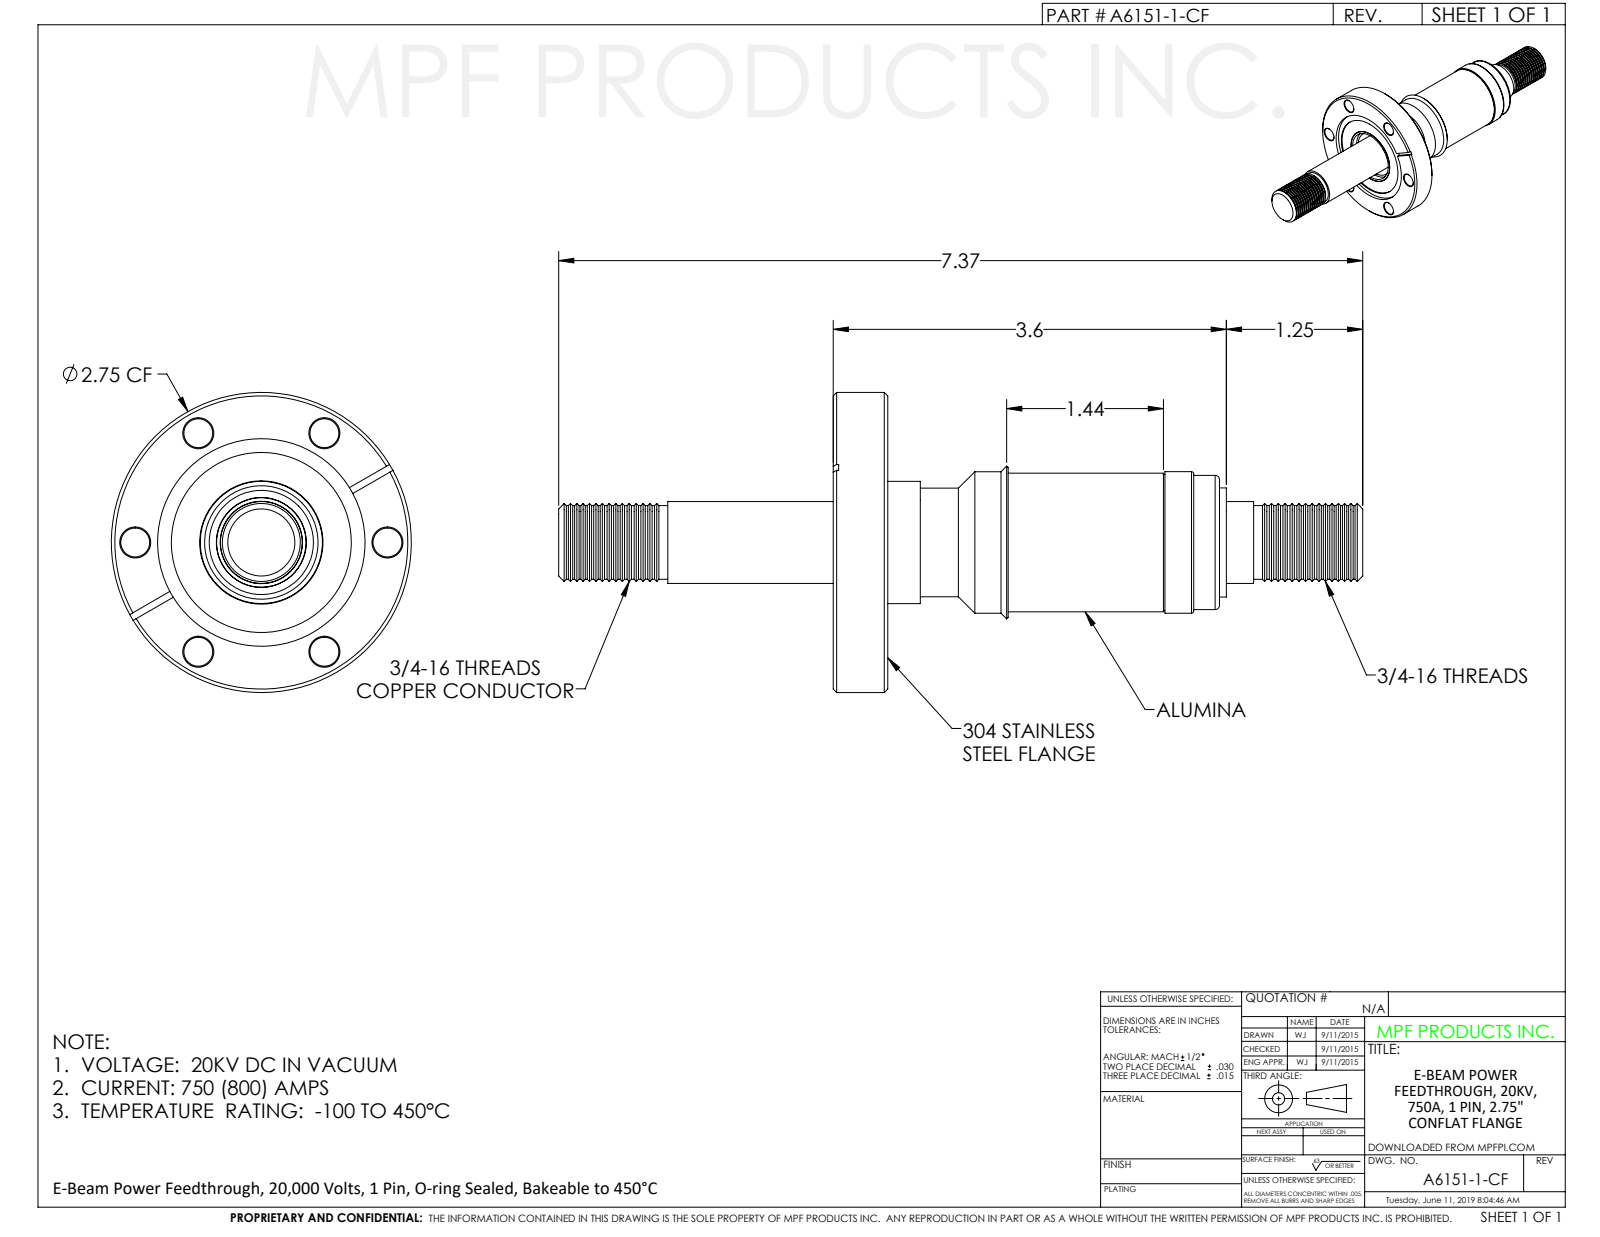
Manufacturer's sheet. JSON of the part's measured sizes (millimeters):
{"part_name": "A6151", "step_written_by": "SolidWorks 2019 (CONFIG_CONTROL_DESIGN)", "units": "millimeters", "bodies": {"solids": 1, "faces": 292, "planar": 21, "cylindrical": 104, "other": 167}, "overall_size": [187.2, 69.9, 69.9], "volume_mm3": 125800, "surface_area_mm2": 28810, "round_holes": [[6.7, 3], [6.7, 3], [22.7, 1], [30.4, 1], [41.9, 1], [48.3, 1]], "round_bosses_or_shafts": [[69.9, 1], [32.9, 1], [32.9, 1], [32.3, 1], [31.8, 1], [31.2, 1], [28.4, 1], [25.4, 1]], "face_to_face_distances": [12.7, 11.5, 1.2, 21.2, 32.6, 33.9, 13.6, 7.6, 19.1, 20.3], "hole_center_spacings": [29.4, 50.9, 50.9, 58.7, 58.7]}
